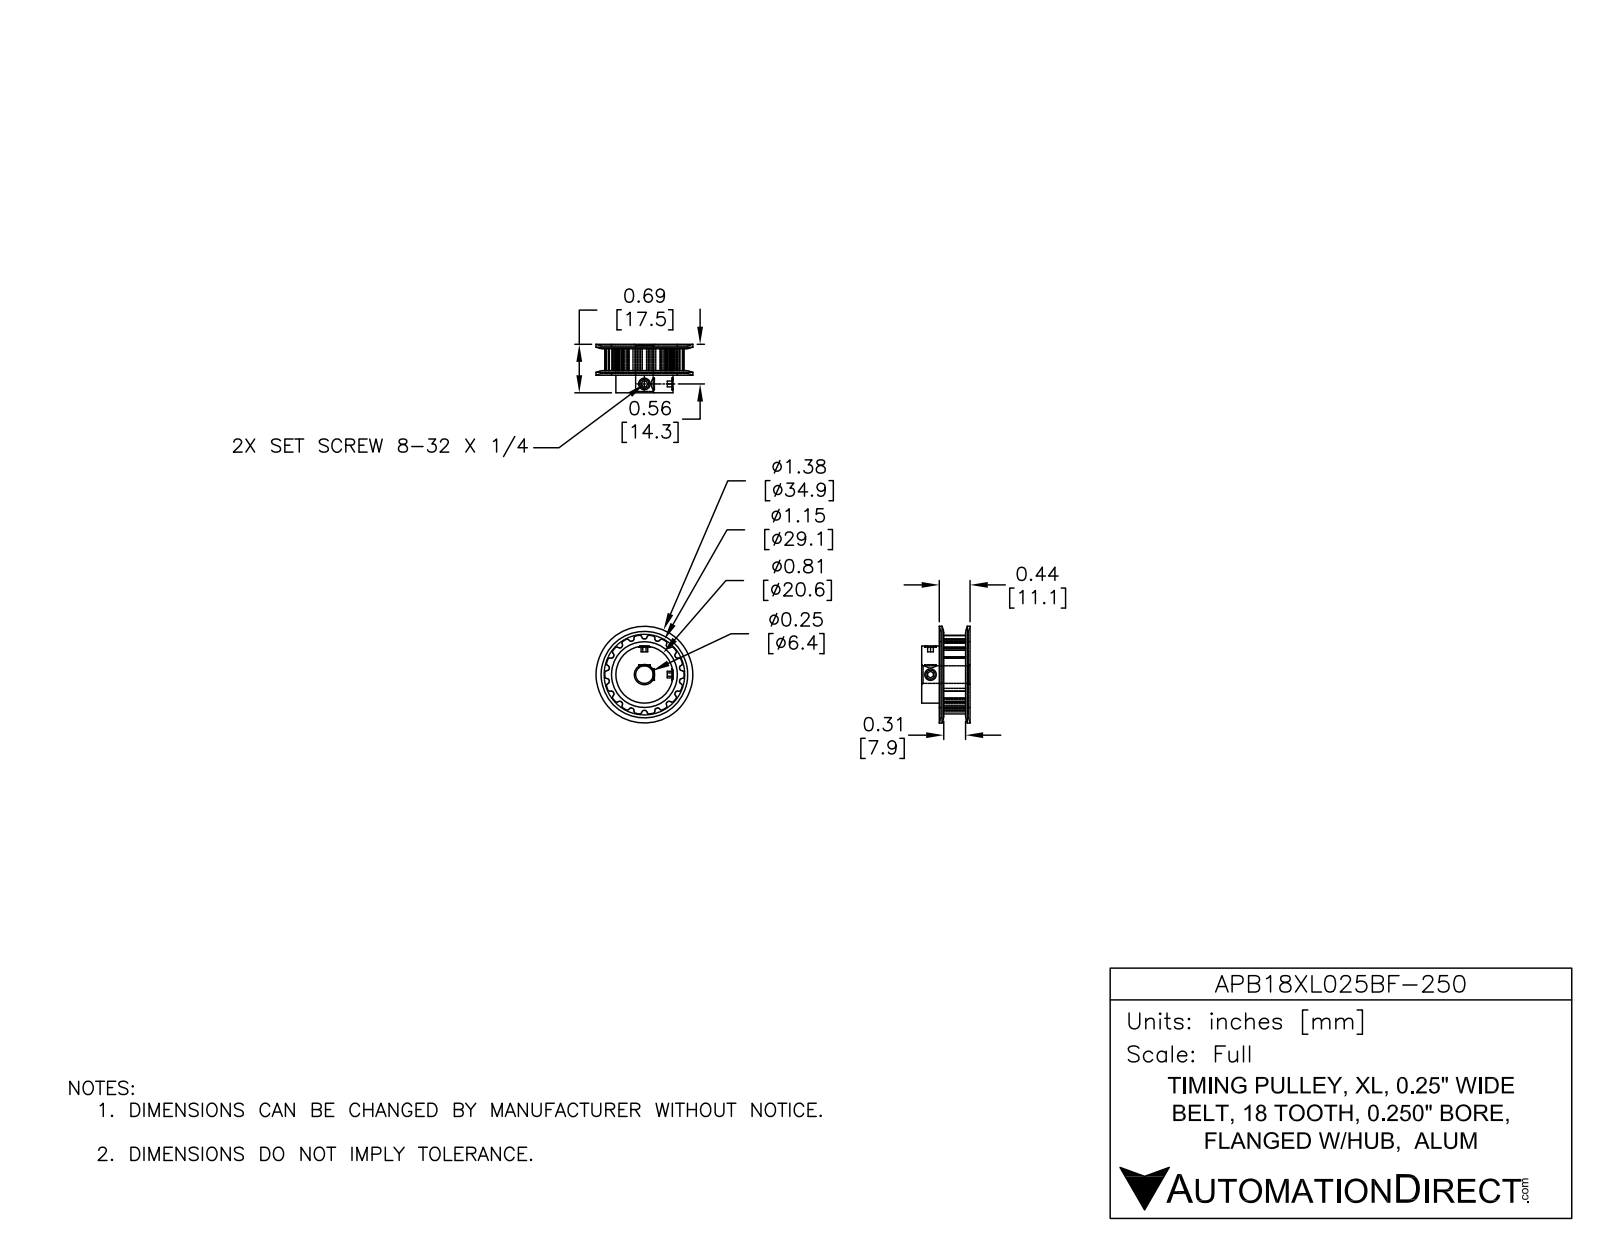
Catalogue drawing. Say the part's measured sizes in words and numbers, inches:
The part is named "APB18XL025BF-250". Its 3-D file was written by "SolidWorks 2014 (AUTOMOTIVE_DESIGN)". It is 1 solid with 196 faces: 60 planar, 114 cylindrical and 22 other. Overall it measures 1.375 by 1.375 by 0.688 inches. Its volume is 0.507 cubic inches and its surface area 7.124 square inches. Round holes: 2 of diameter 0.088, 1 of diameter 0.25. Round bosses or shafts: 1 of diameter 0.813. Partial cylindrical surfaces (rounded edges, fillets, slot ends): 72 of radius 0.015, 1 of radius 0.508. The main face-to-face distances are 0.375, 0.033, 0.407, 0.688, 0.656, 0.281, 1.126, 0.383, 0.342, 0.313.
